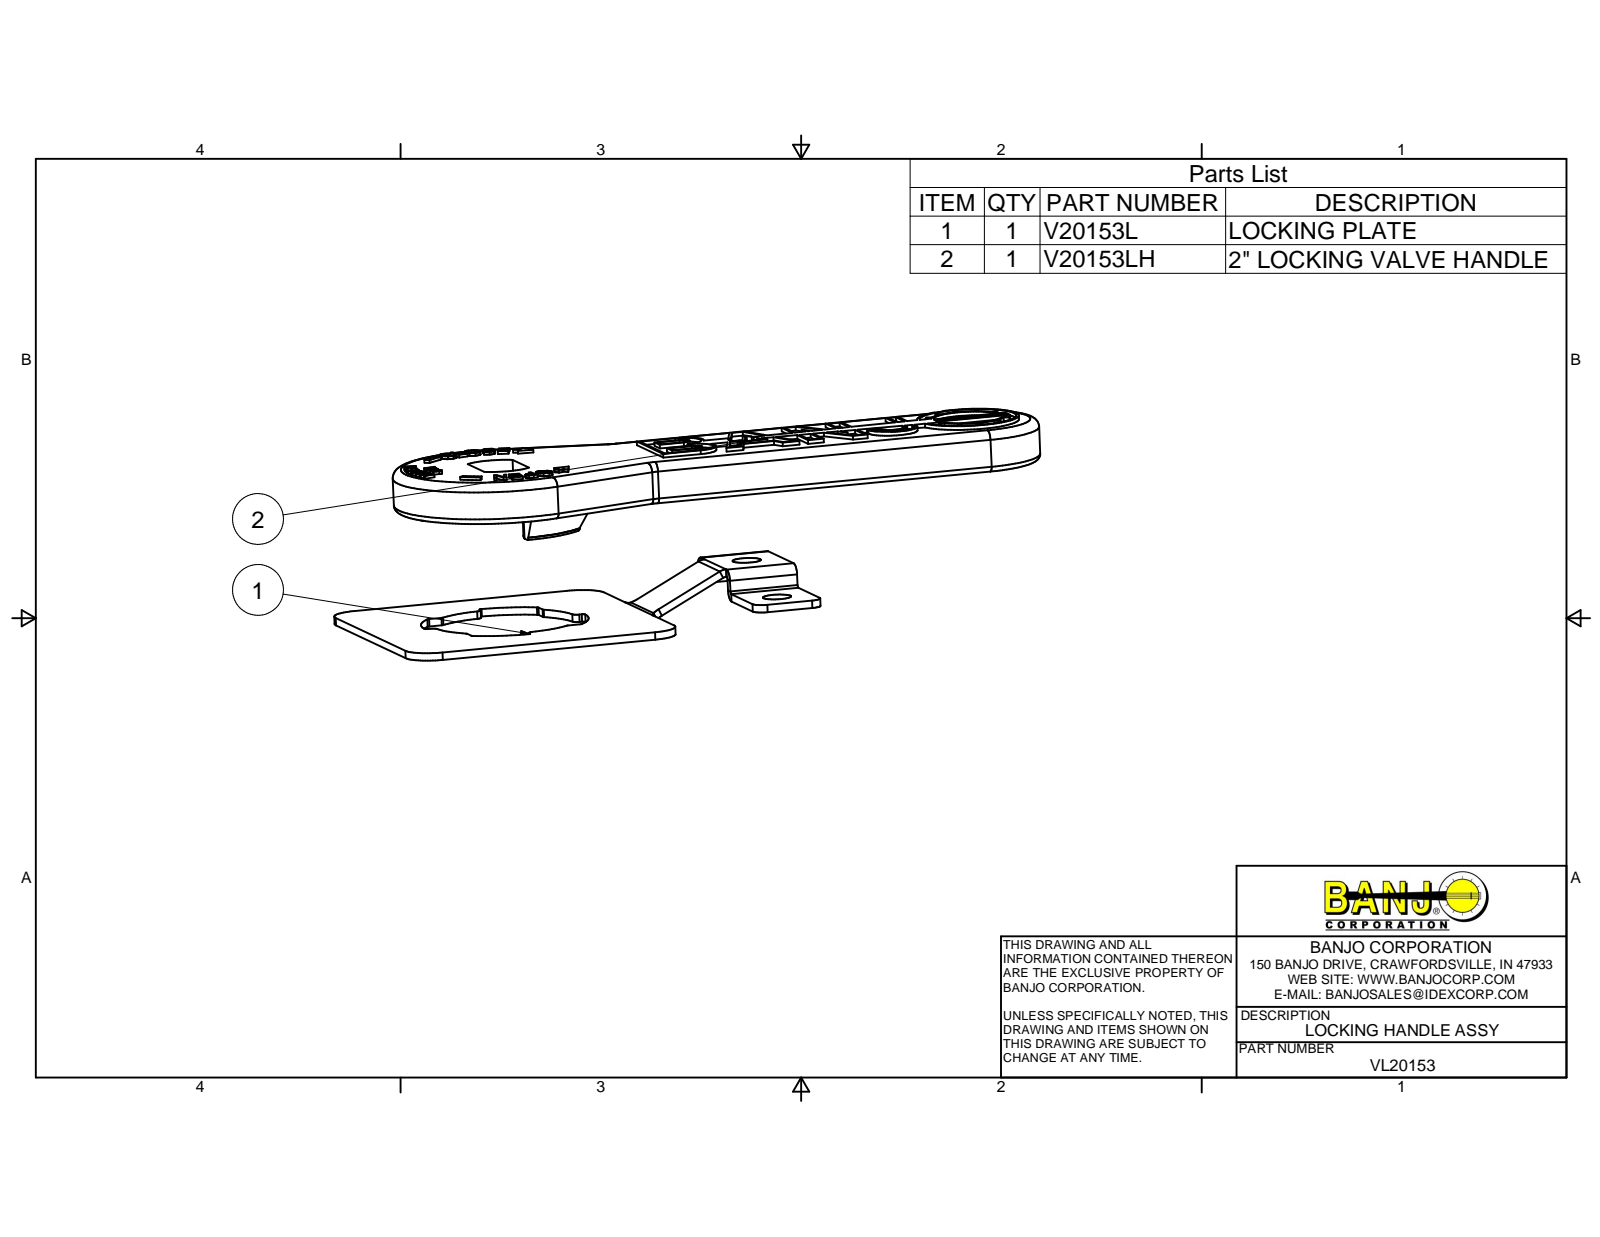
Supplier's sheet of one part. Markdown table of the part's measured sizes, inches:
| quantity | value |
| --- | --- |
| part name | VL20153; V20153L; V20153LH; V20153 |
| STEP written by | Autodesk Inventor 2013 (AUTOMOTIVE_DESIGN) |
| units | inches |
| bodies | 2 solids, 739 faces (449 planar, 138 cylindrical, 152 other) |
| overall size | 7.5 × 3 × 0.8 |
| volume | 4.416 in³ |
| surface area | 55.81 in² |
| round holes (diameter × count) | 0.3 × 2, 0.313 × 1, 0.726 × 1, 1.026 × 1 |
| round bosses / shafts (diameter × count) | 1.25 × 1, 1.08 × 1 |
| partial cylindrical surfaces (radius × count) | 0.03 × 16, 0.09 × 14, 0.06 × 13, 0.125 × 12, 0.313 × 4, 0.025 × 3, 0.105 × 3, 0.063 × 2 |
| main face-to-face distances | 0.08, 0.76, 0.68, 0.245, 0.515, 0.435, 0.32, 0.4, 0.48, 1.5 |
| hole center spacings | 0.06, 0.943, 1.002, 2.511, 2.514, 2.681 |
